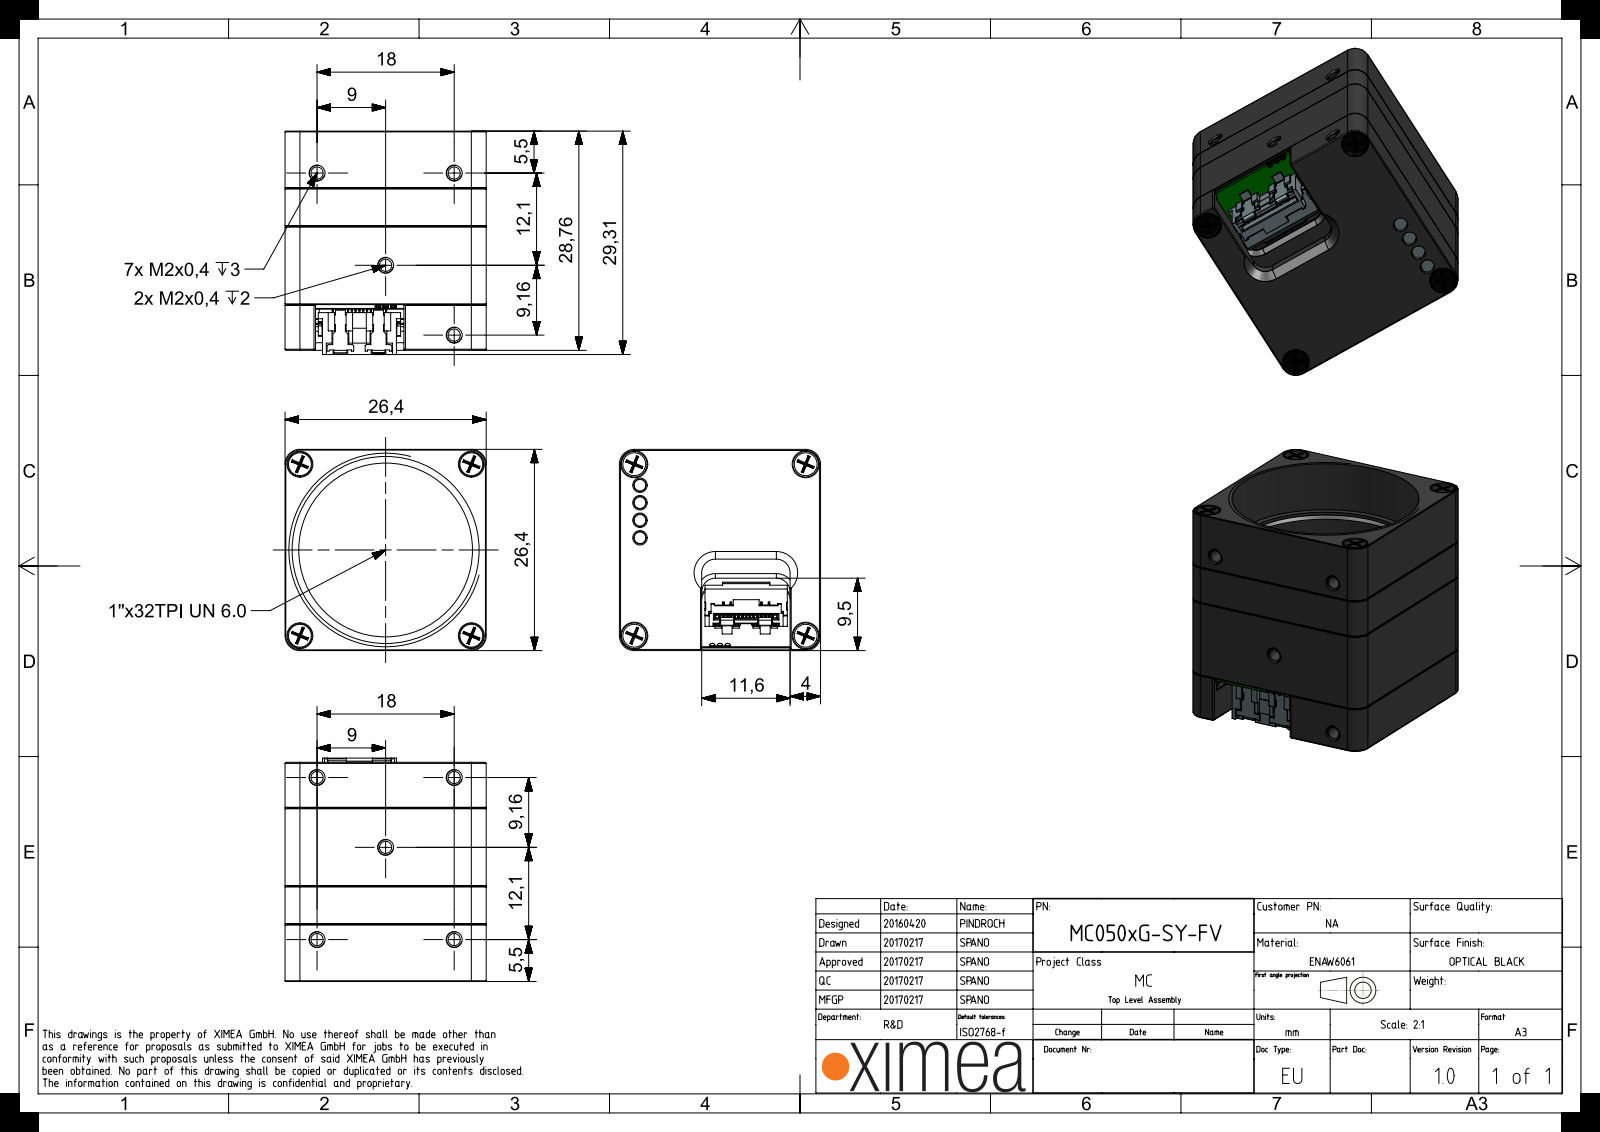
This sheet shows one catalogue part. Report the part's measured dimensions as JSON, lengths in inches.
{"part_name": "MECH-O-RING-22X1-VI370; MT050xG-PR-SENSOR-PCA; FLT-BK7-AR2X-D25; SROB-M1.6x3-SLOT-STNLS (+8 more)", "step_written_by": "SIEMENS PLM Software NX 1907 (AUTOMOTIVE_DESIGN)", "units": "inches", "bodies": {"solids": 32, "faces": 7154, "planar": 4910, "cylindrical": 1953, "other": 291}, "overall_size": [1.154, 1.039, 1.039], "volume_in3": 0.602, "surface_area_in2": 26.79, "round_holes": [[0.063, 13], [0.039, 4], [0.071, 4], [0.079, 4], [0.083, 4], [0.118, 4], [0.126, 4], [0.132, 4], [0.051, 2], [0.073, 1], [0.073, 1], [0.157, 1]], "round_bosses_or_shafts": [[0.075, 4], [0.064, 4], [0.033, 4], [0.118, 2], [0.063, 2], [0.984, 1], [0.85, 1]], "partial_cylinders_radius": [[0.039, 26], [0.013, 16], [0.006, 14], [0.004, 12], [0.015, 12], [0.059, 12], [0.051, 8], [0.008, 7]], "face_to_face_distances": [0.039, 0.138, 1.039, 0.27, 0.304, 0.165, 0.178, 0.447, 0.408, 0.266], "hole_center_spacings": [0.15, 0.508, 0.626, 0.739, 0.869, 0.886, 1.131, 0.091]}
